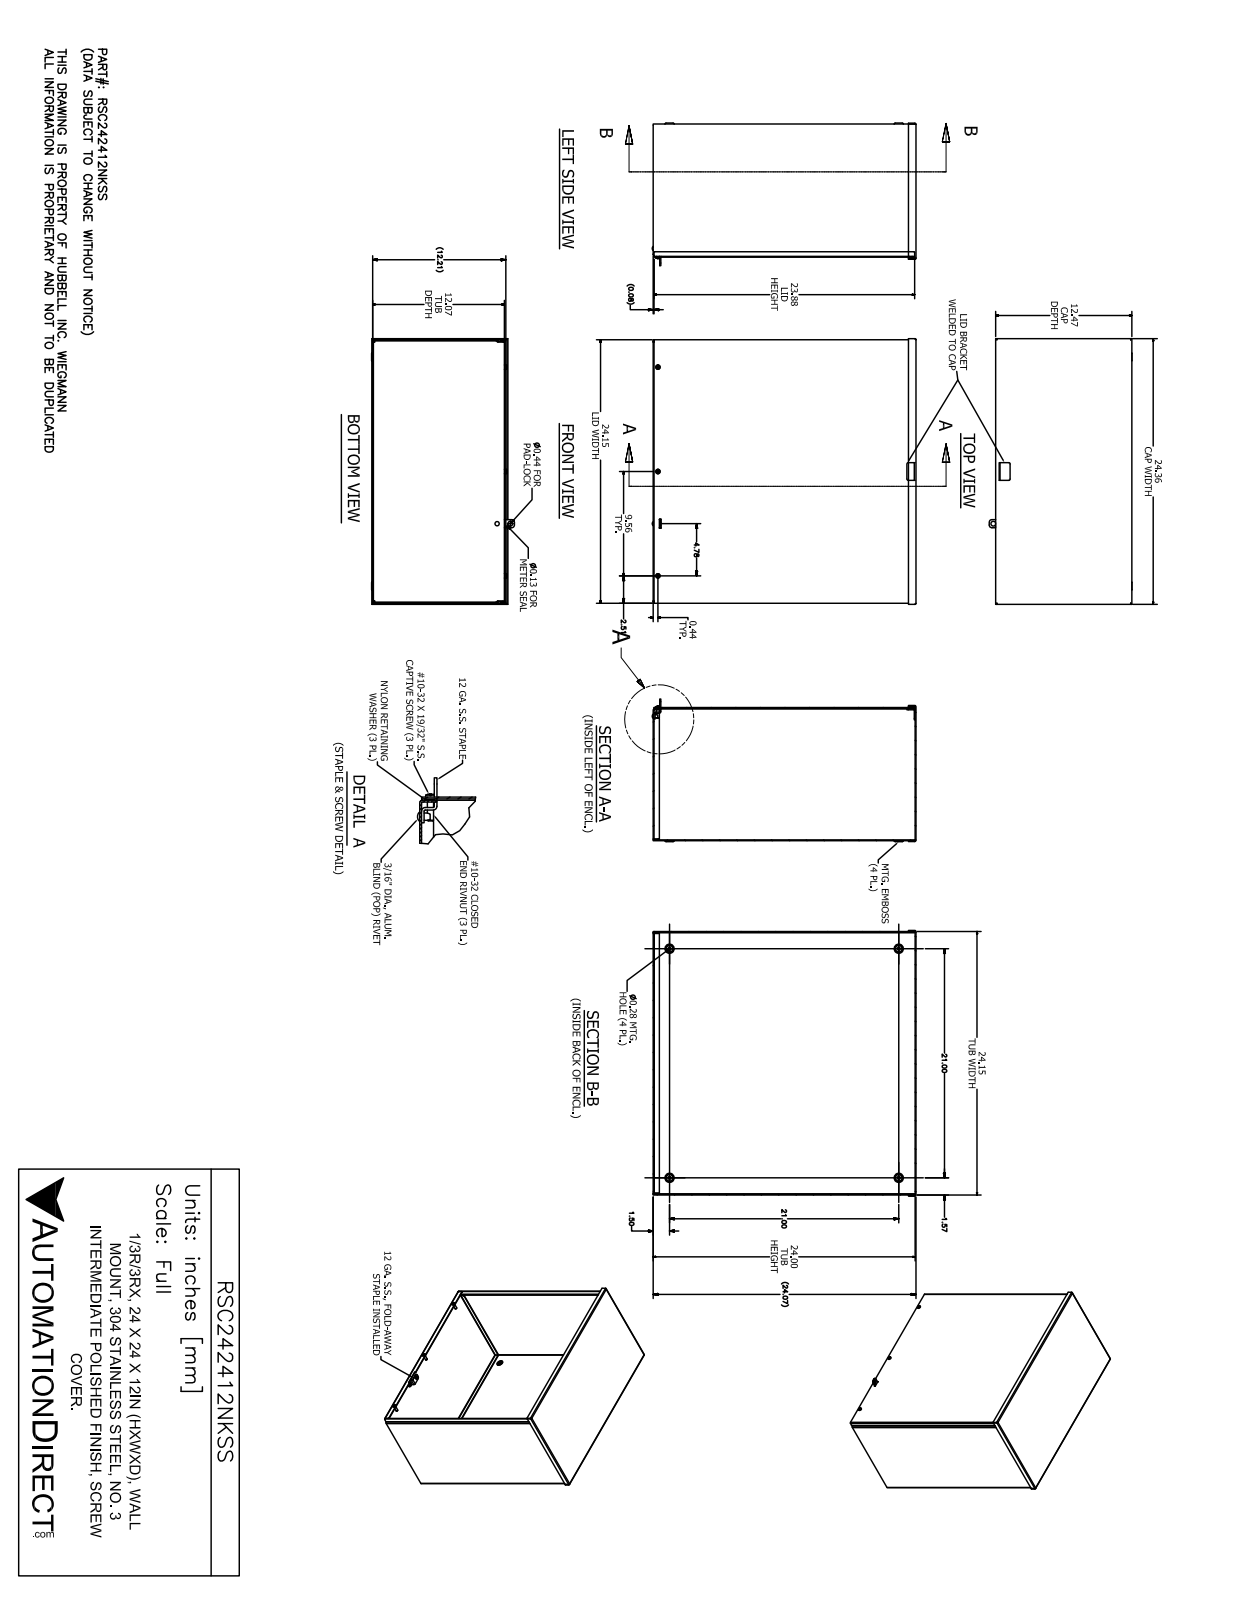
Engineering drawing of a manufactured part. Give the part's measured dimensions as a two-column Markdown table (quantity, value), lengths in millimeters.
| quantity | value |
| --- | --- |
| part name | RSC242412NKSS |
| STEP written by | SolidWorks 2017 (AUTOMOTIVE_DESIGN) |
| units | millimeters |
| bodies | 16 solids, 458 faces (237 planar, 113 cylindrical, 108 other) |
| overall size | 618.7 × 613.8 × 332.3 |
| volume | 2 943 000 mm³ |
| surface area | 3 152 000 mm² |
| round holes (diameter × count) | 6.4 × 6, 7.1 × 4, 4 × 3, 5 × 3, 6.5 × 3, 7.1 × 3, 3.2 × 1, 5 × 1, 5.1 × 1, 11.1 × 1 |
| round bosses / shafts (diameter × count) | 11.5 × 3, 10.3 × 3, 6.3 × 3, 4.2 × 3, 4.7 × 1 |
| partial cylindrical surfaces (radius × count) | 0.8 × 23, 2.7 × 17, 3.2 × 4, 6.4 × 4, 1.6 × 3, 2.3 × 3, 1.2 × 2, 1.3 × 2 |
| main face-to-face distances | 1.9, 308.2, 609.6, 611.5, 310, 306.3, 607.7, 613.4, 2.9, 608.6 |
| hole center spacings | 242.9, 533.4, 636.3, 588.2, 36, 36.6, 268.1, 268.1 |
